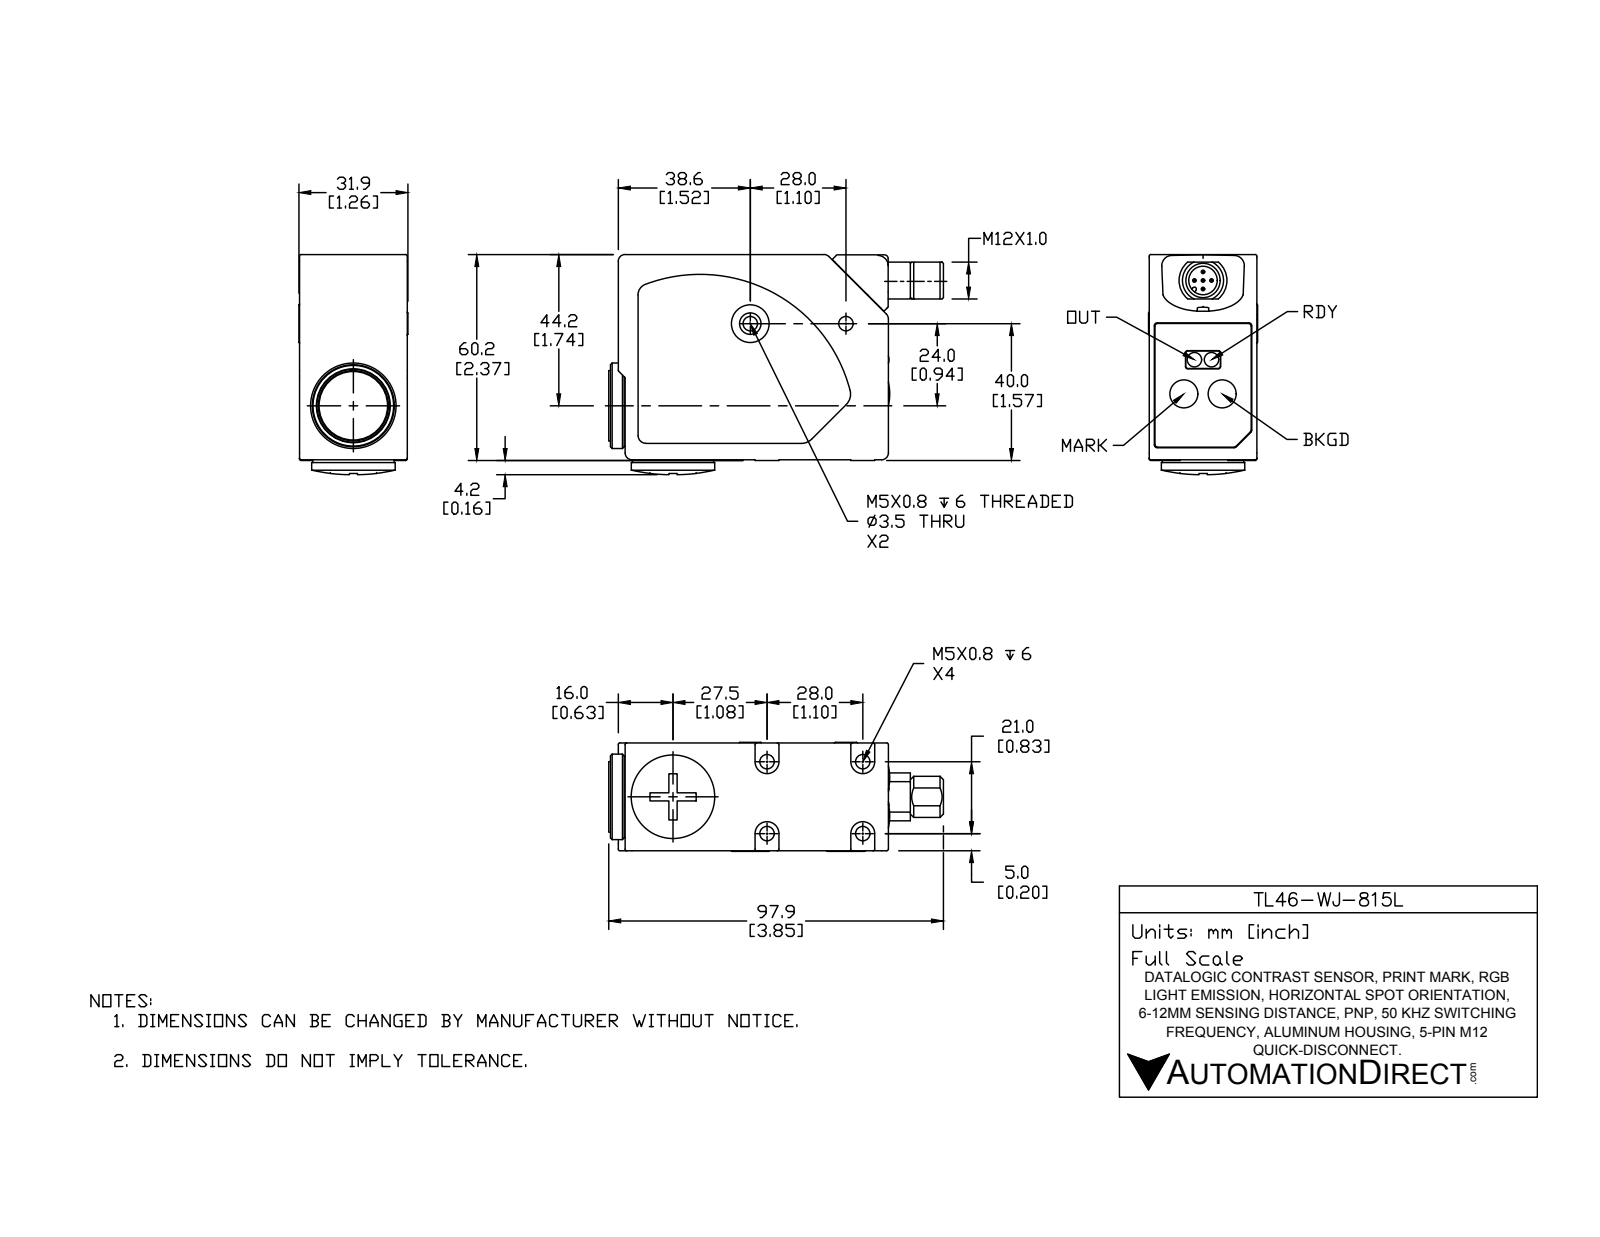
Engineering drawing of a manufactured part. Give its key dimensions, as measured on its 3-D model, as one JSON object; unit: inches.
{"part_name": "TL46-WJ-815L", "step_written_by": "SolidWorks 2016 (AUTOMOTIVE_DESIGN)", "units": "inches", "bodies": {"solids": 7, "faces": 332, "planar": 96, "cylindrical": 128, "other": 108}, "overall_size": [3.854, 2.534, 1.256], "volume_in3": 9.069, "surface_area_in2": 33.48, "round_holes": [[0.165, 8], [0.323, 2], [0.327, 1], [0.787, 1]], "round_bosses_or_shafts": [[0.039, 5], [0.937, 2], [0.984, 1], [0.961, 1], [0.748, 1], [0.433, 1]], "partial_cylinders_radius": [[0.02, 32], [0.031, 10], [0.024, 5], [0.079, 5], [0.02, 4], [0.138, 4], [0.236, 1], [0.276, 1]], "face_to_face_distances": [1.232, 1.224, 1.24, 2.362, 3.11, 3.031, 0.079, 0.016, 1.248, 2.37], "hole_center_spacings": [1.102, 0.259, 0.412, 0.507, 0.539, 0.827, 0.917, 1.324]}
